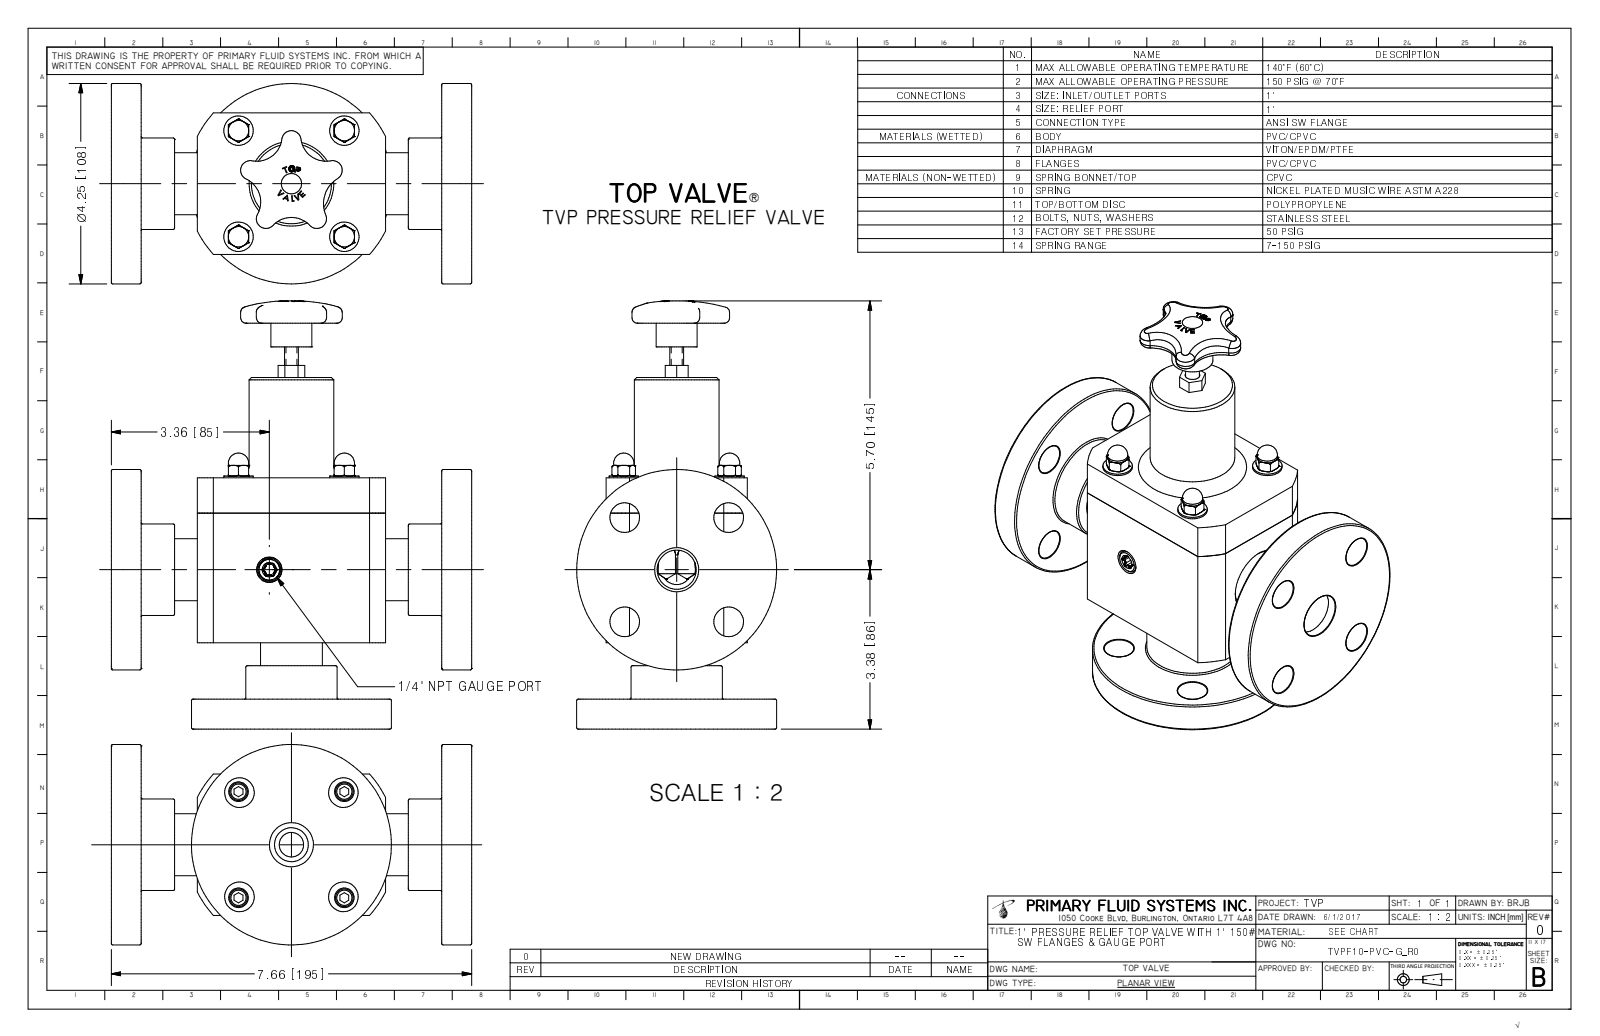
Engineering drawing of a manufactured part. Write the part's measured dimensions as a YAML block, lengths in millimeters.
part_name: "TVPF10-PVC-G_R0"
step_written_by: "Autodesk Inventor 2009 (AUTOMOTIVE_DESIGN)"
units: millimeters
bodies: {solids: 1, faces: 450, planar: 167, cylindrical: 78, other: 205}
overall_size: [230.6, 194.6, 108]
volume: 1224000
surface_area: 184000
round_holes:
  - {diameter: 16, count: 8}
  - {diameter: 4.4, count: 4}
  - {diameter: 23.8, count: 2}
  - {diameter: 24.3, count: 2}
  - {diameter: 64.1, count: 1}
round_bosses_or_shafts:
  - {diameter: 15.9, count: 4}
  - {diameter: 11, count: 4}
  - {diameter: 9.5, count: 4}
  - {diameter: 108, count: 2}
  - {diameter: 49.3, count: 2}
  - {diameter: 33.4, count: 2}
  - {diameter: 63.5, count: 1}
  - {diameter: 45.7, count: 1}
partial_cylinders:
  - {radius: 0.7, count: 6}
  - {radius: 2.2, count: 5}
  - {radius: 5.2, count: 5}
  - {radius: 13.6, count: 4}
  - {radius: 16.7, count: 4}
  - {radius: 15.9, count: 1}
  - {radius: 18.9, count: 1}
  - {radius: 56.8, count: 1}
face_to_face_distances: [16.1, 46.5, 30.4, 178.4, 194.6, 76.2, 148.1, 132, 162.3, 135.4]
hole_center_spacings: [39.7, 56.1, 56.6, 56.6, 57.2, 79.4, 80.1, 0.7]
